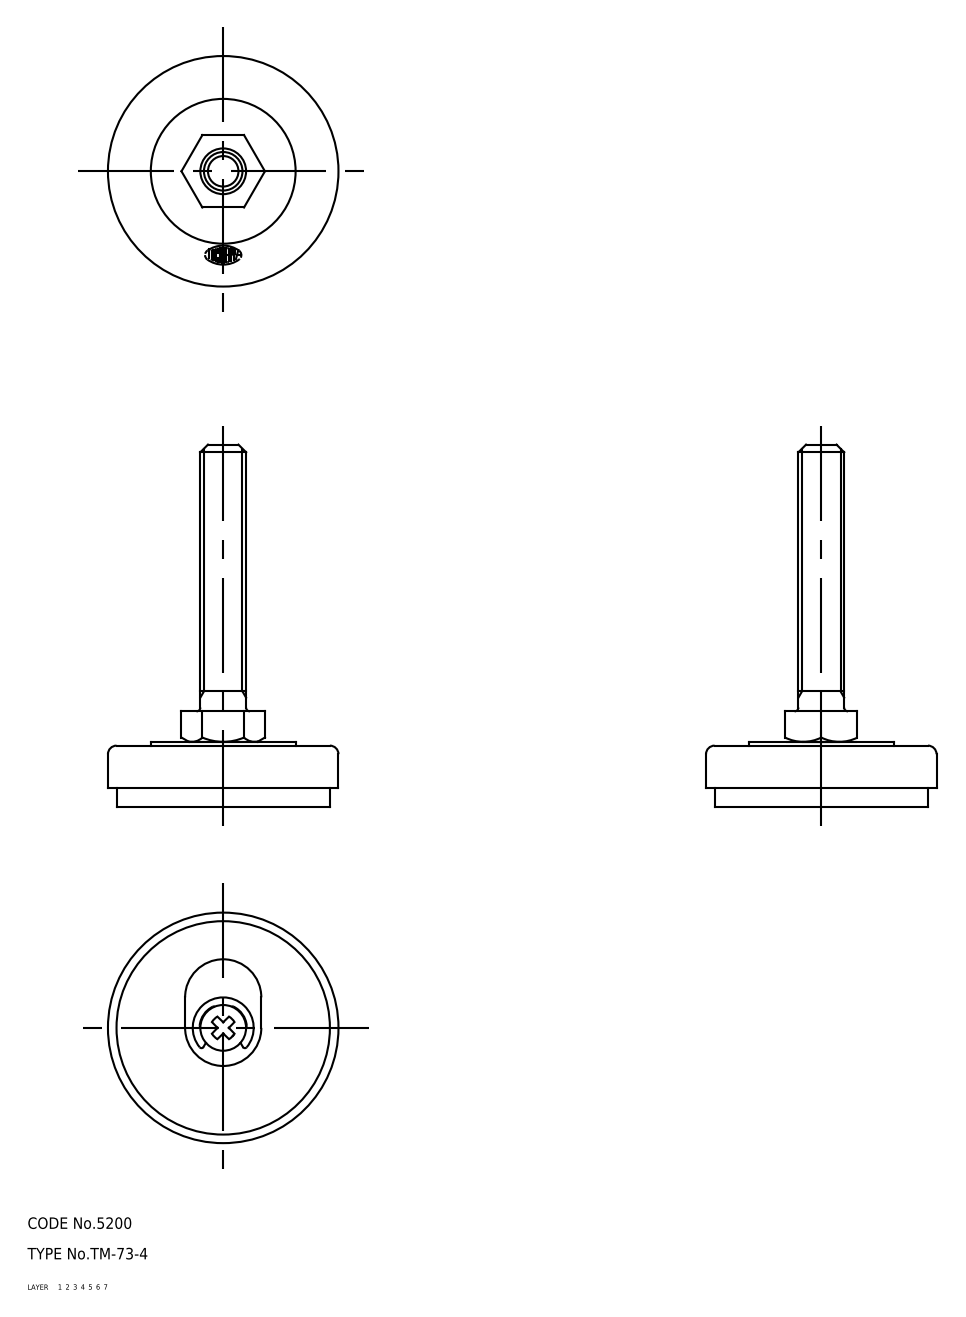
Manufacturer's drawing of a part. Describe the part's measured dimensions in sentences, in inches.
The part is named "washer; rubber pad; retainer; cover (+3 more)". Its 3-D file was written by "CADfix (AUTOMOTIVE_DESIGN)". It is 6 solids with 121 faces: 0 planar, 0 cylindrical and 121 other. Overall it measures 3.74 by 2.382 by 2.382 inches. Its volume is 3.173 cubic inches and its surface area 46.64 square inches.
